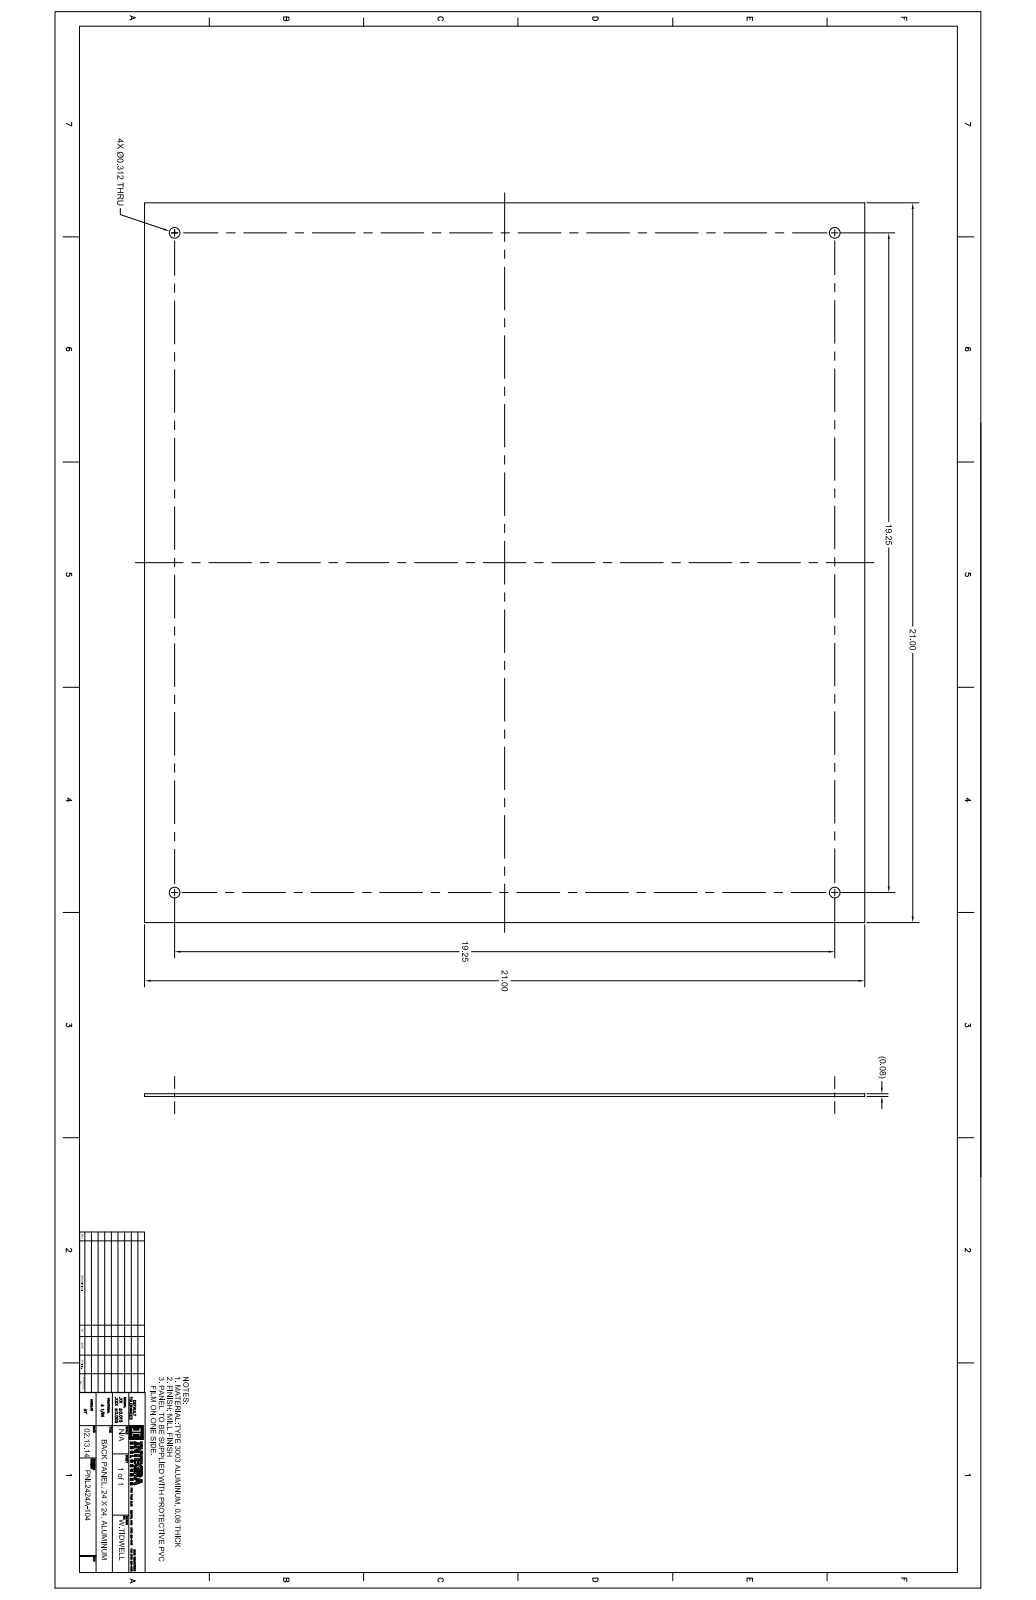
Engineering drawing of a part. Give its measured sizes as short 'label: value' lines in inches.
name: ABP-2424-P10
written by: SolidWorks 2018 (AUTOMOTIVE_DESIGN)
unit: in
bodies: 1 solid, 10 faces (6 planar, 4 cylindrical, 0 other)
size: 21 × 21 × 0.08
volume: 35.26 in³; area: 888.4 in²
holes: 4× ⌀0.312
face distances: 0.08, 21
hole spacings: 19.25, 27.223
